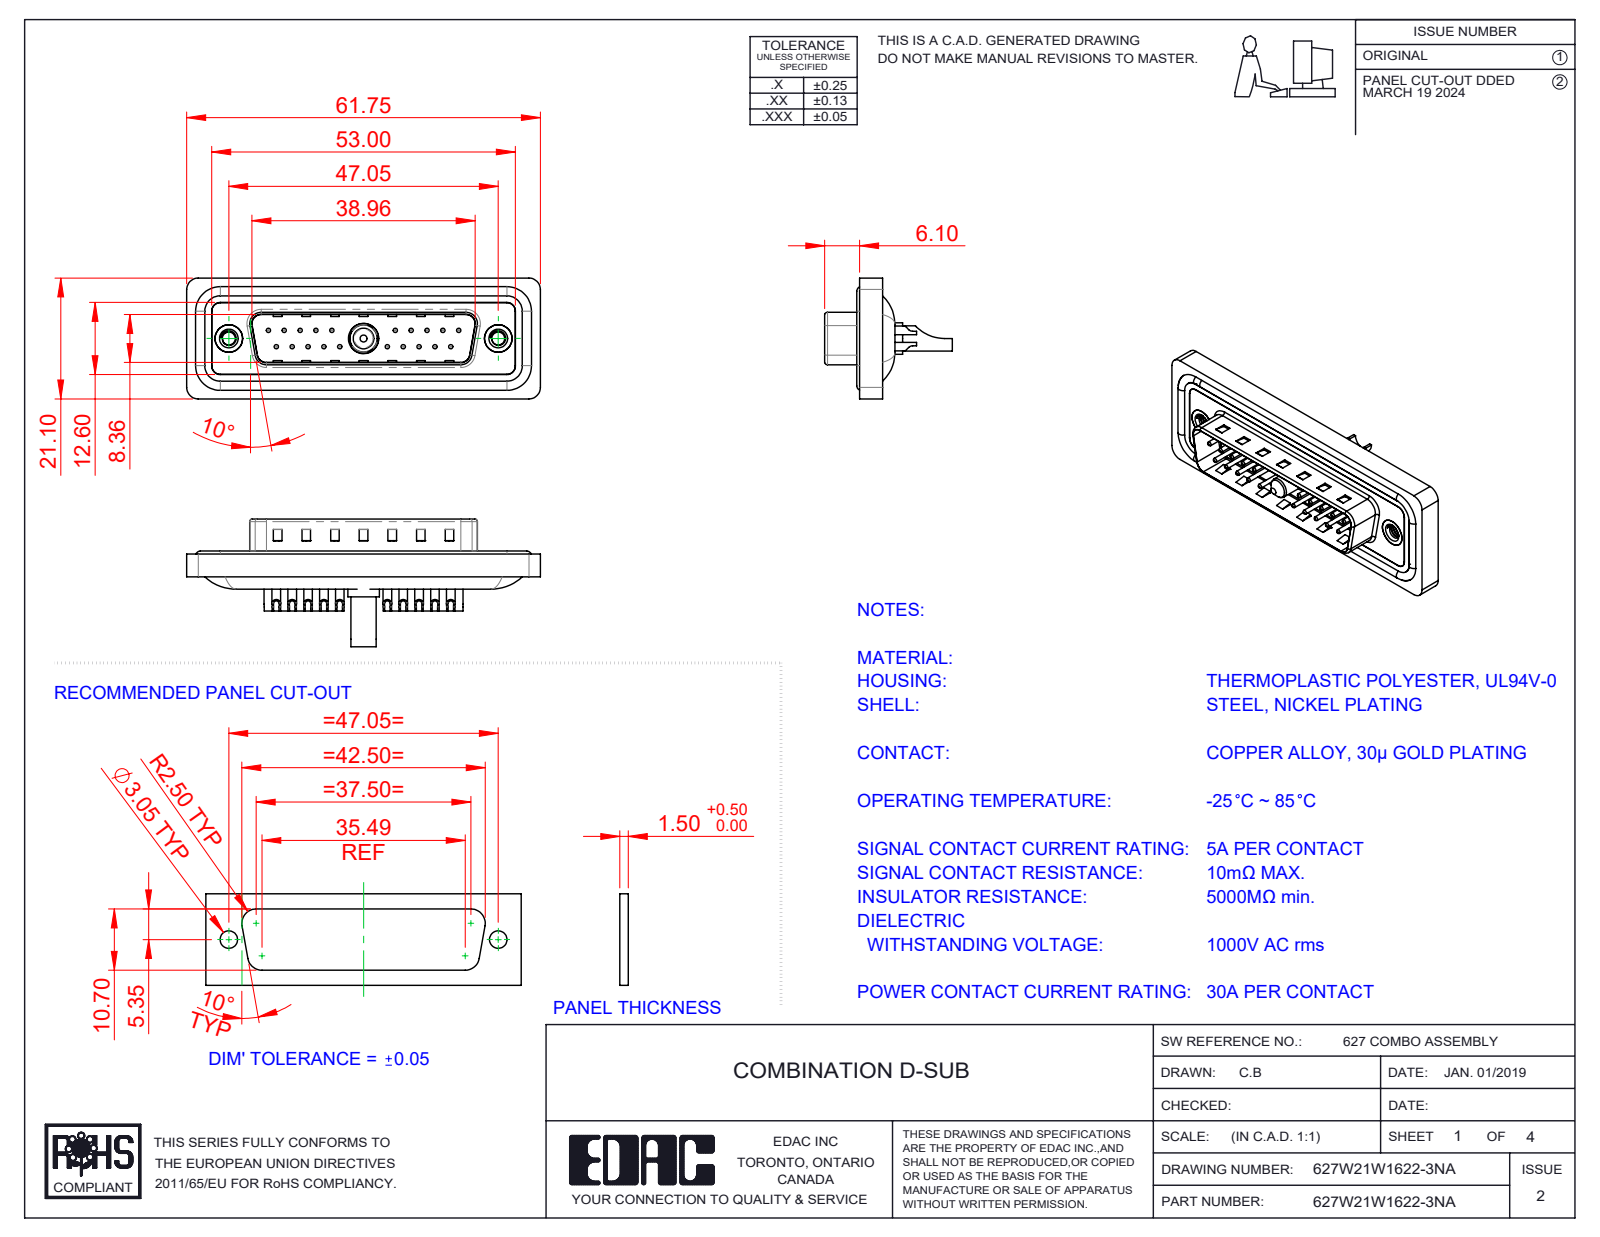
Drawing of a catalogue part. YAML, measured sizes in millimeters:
part_name: "627Combo Threaded Rivet_A; 627Combo Waterproof Housing_25 Contacts; Power Pin_30A SC; 627Combo Shell Front_25 Contacts (+5 more)"
step_written_by: "SolidWorks 2023 (CONFIG_CONTROL_DESIGN)"
units: millimeters
bodies: {solids: 29, faces: 1266, planar: 402, cylindrical: 532, other: 332}
overall_size: [61.75, 22.3, 21.1]
volume: 7254
surface_area: 12218
round_holes:
  - {diameter: 0.75, count: 20}
  - {diameter: 1, count: 20}
  - {diameter: 1.6, count: 20}
  - {diameter: 2, count: 20}
  - {diameter: 2.26, count: 2}
  - {diameter: 4, count: 2}
  - {diameter: 4.8, count: 2}
  - {diameter: 5, count: 2}
  - {diameter: 3.5, count: 1}
  - {diameter: 4.85, count: 1}
  - {diameter: 5.3, count: 1}
round_bosses_or_shafts:
  - {diameter: 1.5, count: 20}
  - {diameter: 1.6, count: 4}
  - {diameter: 4.9, count: 2}
  - {diameter: 5.5, count: 1}
  - {diameter: 5.2, count: 1}
  - {diameter: 4.75, count: 1}
  - {diameter: 4.4, count: 1}
  - {diameter: 3.75, count: 1}
partial_cylinders:
  - {radius: 1.5, count: 22}
  - {radius: 2, count: 18}
  - {radius: 0.5, count: 8}
  - {radius: 1.6, count: 8}
  - {radius: 1, count: 6}
  - {radius: 0.25, count: 4}
  - {radius: 0.6, count: 4}
  - {radius: 0.65, count: 4}
face_to_face_distances: [0.4, 1.5, 1.1, 1.6, 0.5, 3.1, 2.9, 4.1, 0.82, 9.58]
hole_center_spacings: [3.16, 2.77, 5.54, 8.31, 5.04, 19.39, 20.97, 22.16]
